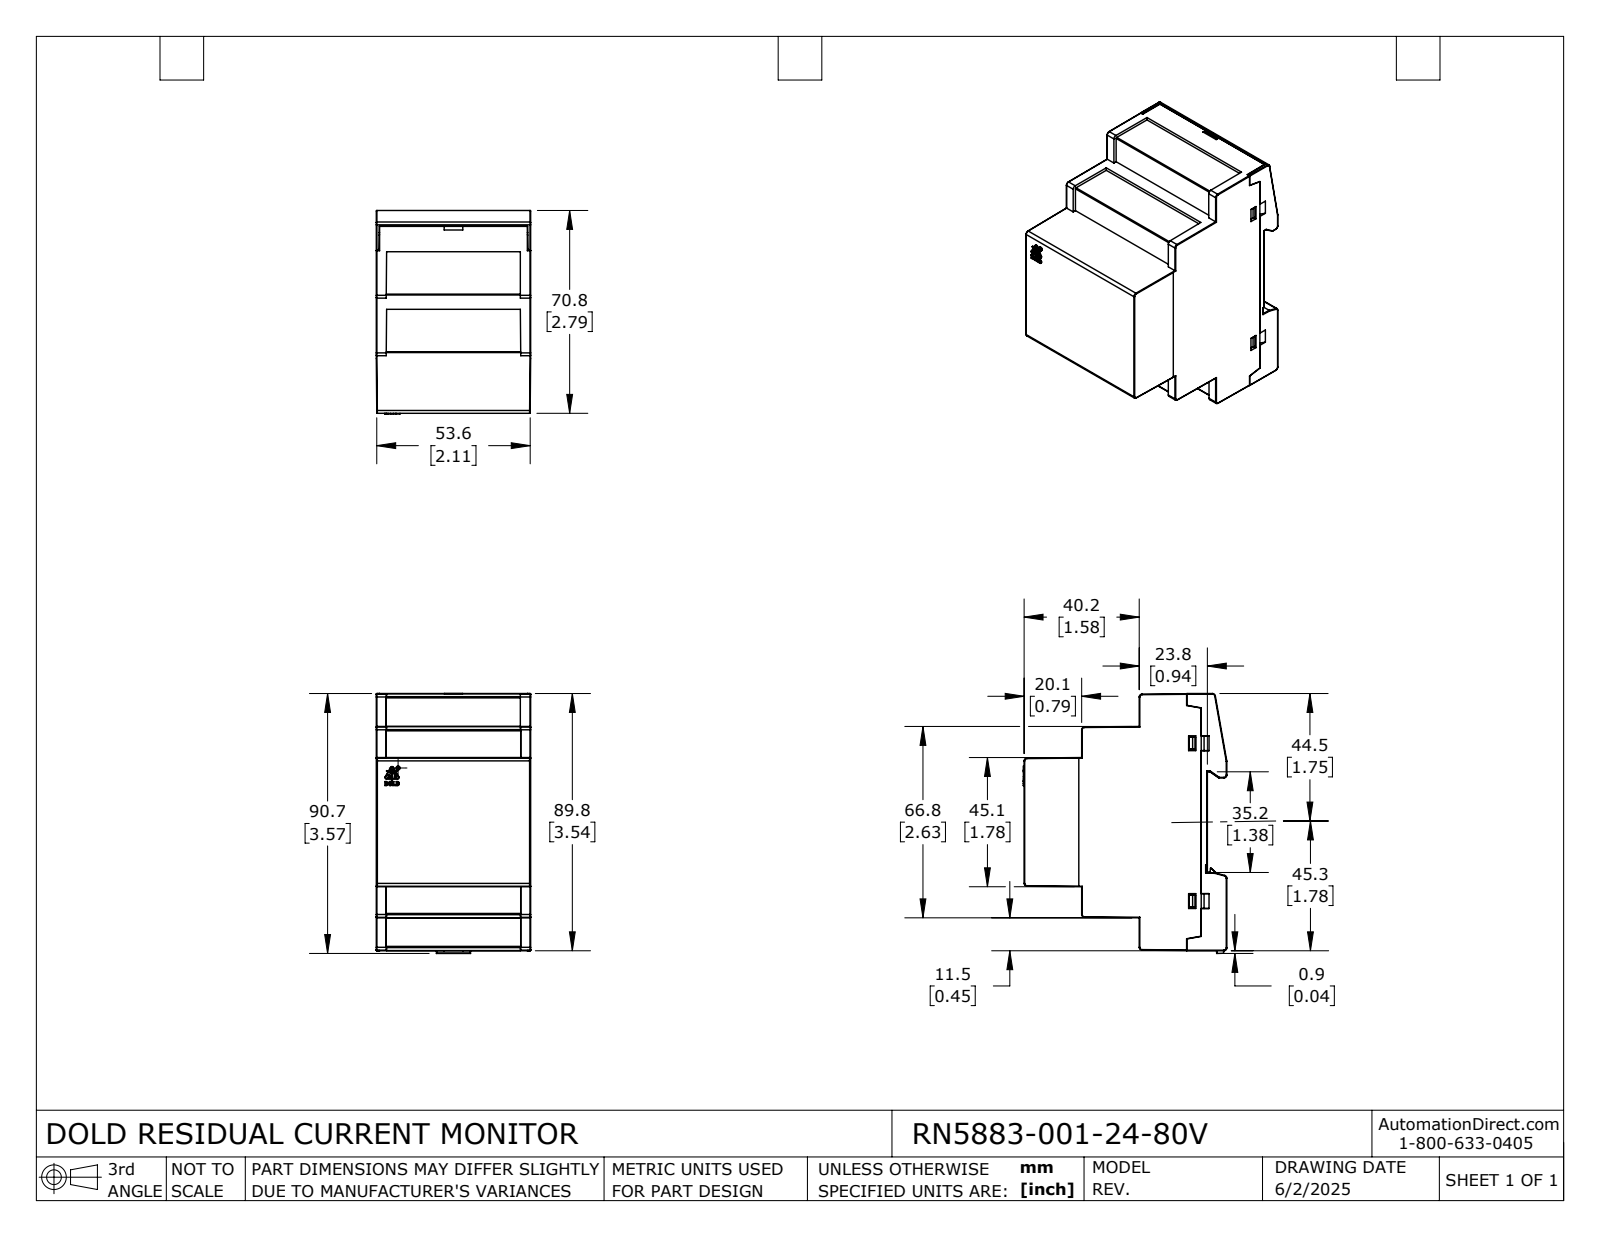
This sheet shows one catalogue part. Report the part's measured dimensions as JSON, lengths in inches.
{"part_name": "RN5883-001-24-80V", "step_written_by": "SolidWorks 2024 (AUTOMOTIVE_DESIGN)", "units": "inches", "bodies": {"solids": 13, "faces": 1307, "planar": 1035, "cylindrical": 186, "other": 86}, "overall_size": [3.572, 2.797, 2.122], "volume_in3": 14.21, "surface_area_in2": 80.85, "round_holes": [[0.049, 1]], "round_bosses_or_shafts": [[0.098, 6], [0.157, 4], [0.181, 1], [0.053, 1]], "partial_cylinders_radius": [[0.008, 44], [0.004, 19], [0.039, 18], [0.02, 11], [0.005, 6], [0.004, 4], [0.012, 4], [0.021, 3]], "face_to_face_distances": [0.136, 2.122, 1.986, 0.063, 0.073, 2.049, 1.913, 0.041, 2.435, 0.085]}
